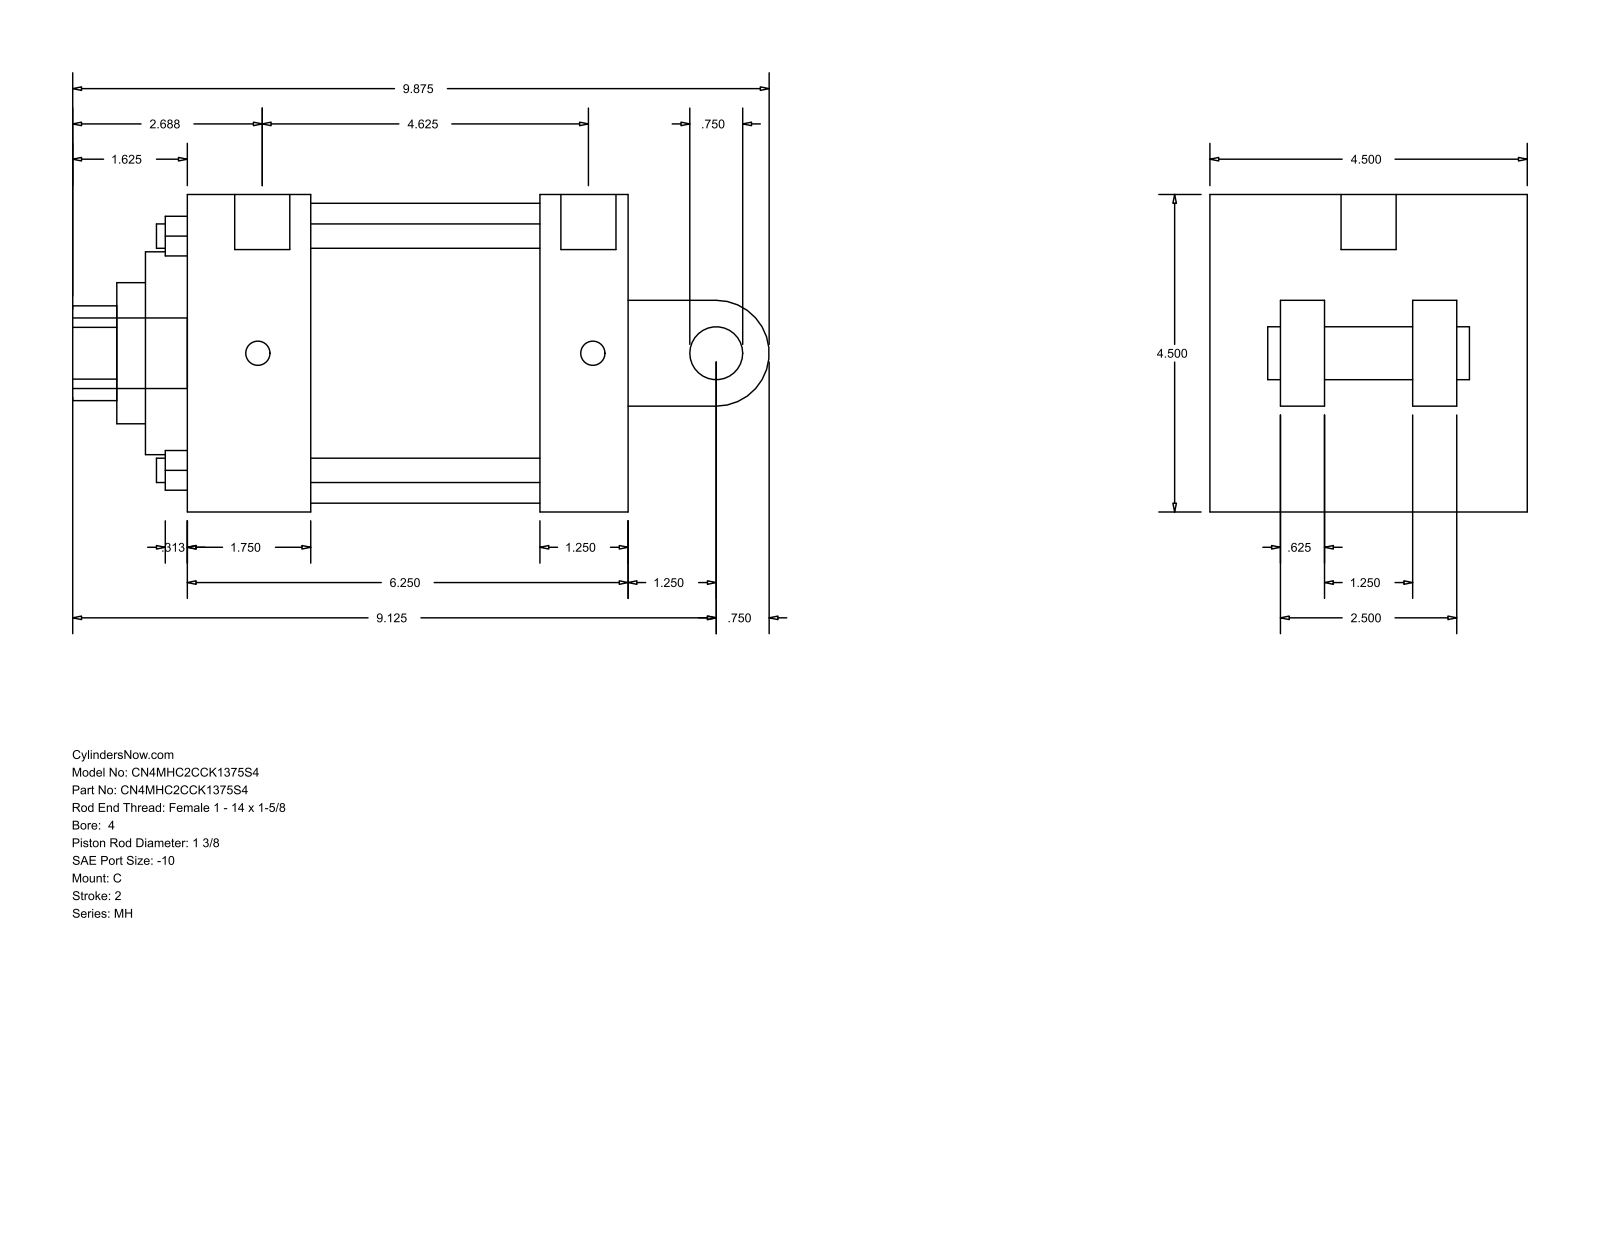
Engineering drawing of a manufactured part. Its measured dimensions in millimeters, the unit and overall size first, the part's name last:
Units: millimetres
Overall size (bounding box): 250.82 × 114.3 × 114.3
Round holes (diameter × count): ⌀8.76 ×4, ⌀8.73 ×2, ⌀19.84 ×1, ⌀34.92 ×1, ⌀50.8 ×1, ⌀73.03 ×1, ⌀107.95 ×1
Round bosses / shafts (diameter × count): ⌀8.73 ×2, ⌀25.4 ×1, ⌀19.84 ×1, ⌀19.05 ×1
Partial cylindrical surfaces — rounded edges, fillets, slot ends (radius × count): R17.06 ×1, R19.05 ×1
Main face-to-face distances: 114.3, 158.76, 44.45, 127.01, 82.56, 114.31, 31.75, 73.03, 41.27, 38.1
Hole centre spacings: 59.62, 84.32, 119.25, 1.58
Bodies: 0 solids, 101 faces (71 planar, 30 cylindrical, 0 other)
Part name (STEP PRODUCT): MH_C__0400_1.375
STEP written by: GSSL Pune (CONFIG_CONTROL_DESIGN)
